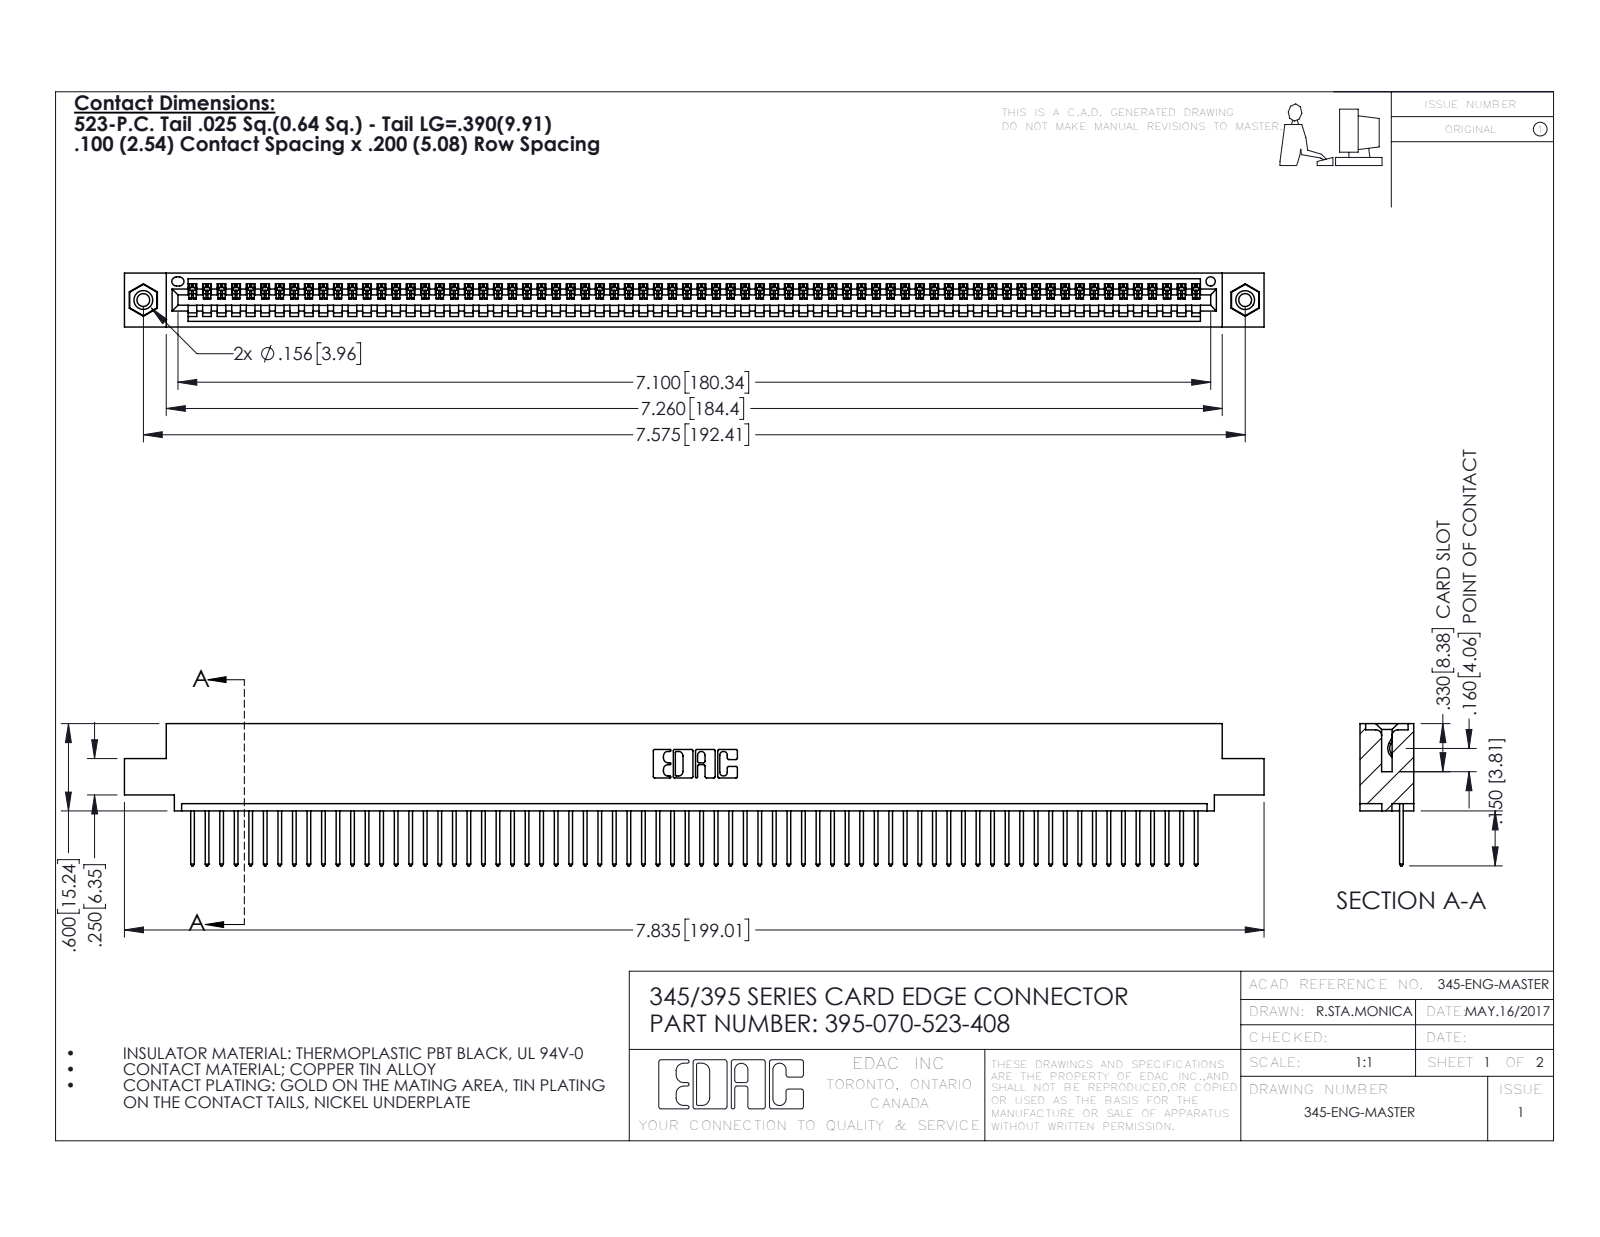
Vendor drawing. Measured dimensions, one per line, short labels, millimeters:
name: 345 Part_0.110 Offset - 0.156 Dia-TI; 345-250-001_345-250-003-102; 395-070-523-408; 345-292-001_345-293-123
written by: SolidWorks 2016 (CONFIG_CONTROL_DESIGN)
unit: mm
bodies: 73 solids, 4250 faces (2916 planar, 1318 cylindrical, 16 other)
size: 199 × 24.8 × 9.4
volume: 19 030 mm³; area: 25 840 mm²
holes: 2× ⌀2.3, 2× ⌀3.2, 2× ⌀4, 1× ⌀1.6
bosses: 2× ⌀3.9
rounds: 140× R0.2, 140× R0.3, 22× R0.3, 6× R0.2, 6× R0.8, 3× R0.7, 2× R0.8, 2× R1
face distances: 1.8, 7.6, 9.4, 5.1, 2.5, 6.9, 0.6, 5.7, 3.8, 1.8
hole spacings: 6.9, 186.4, 192.4
